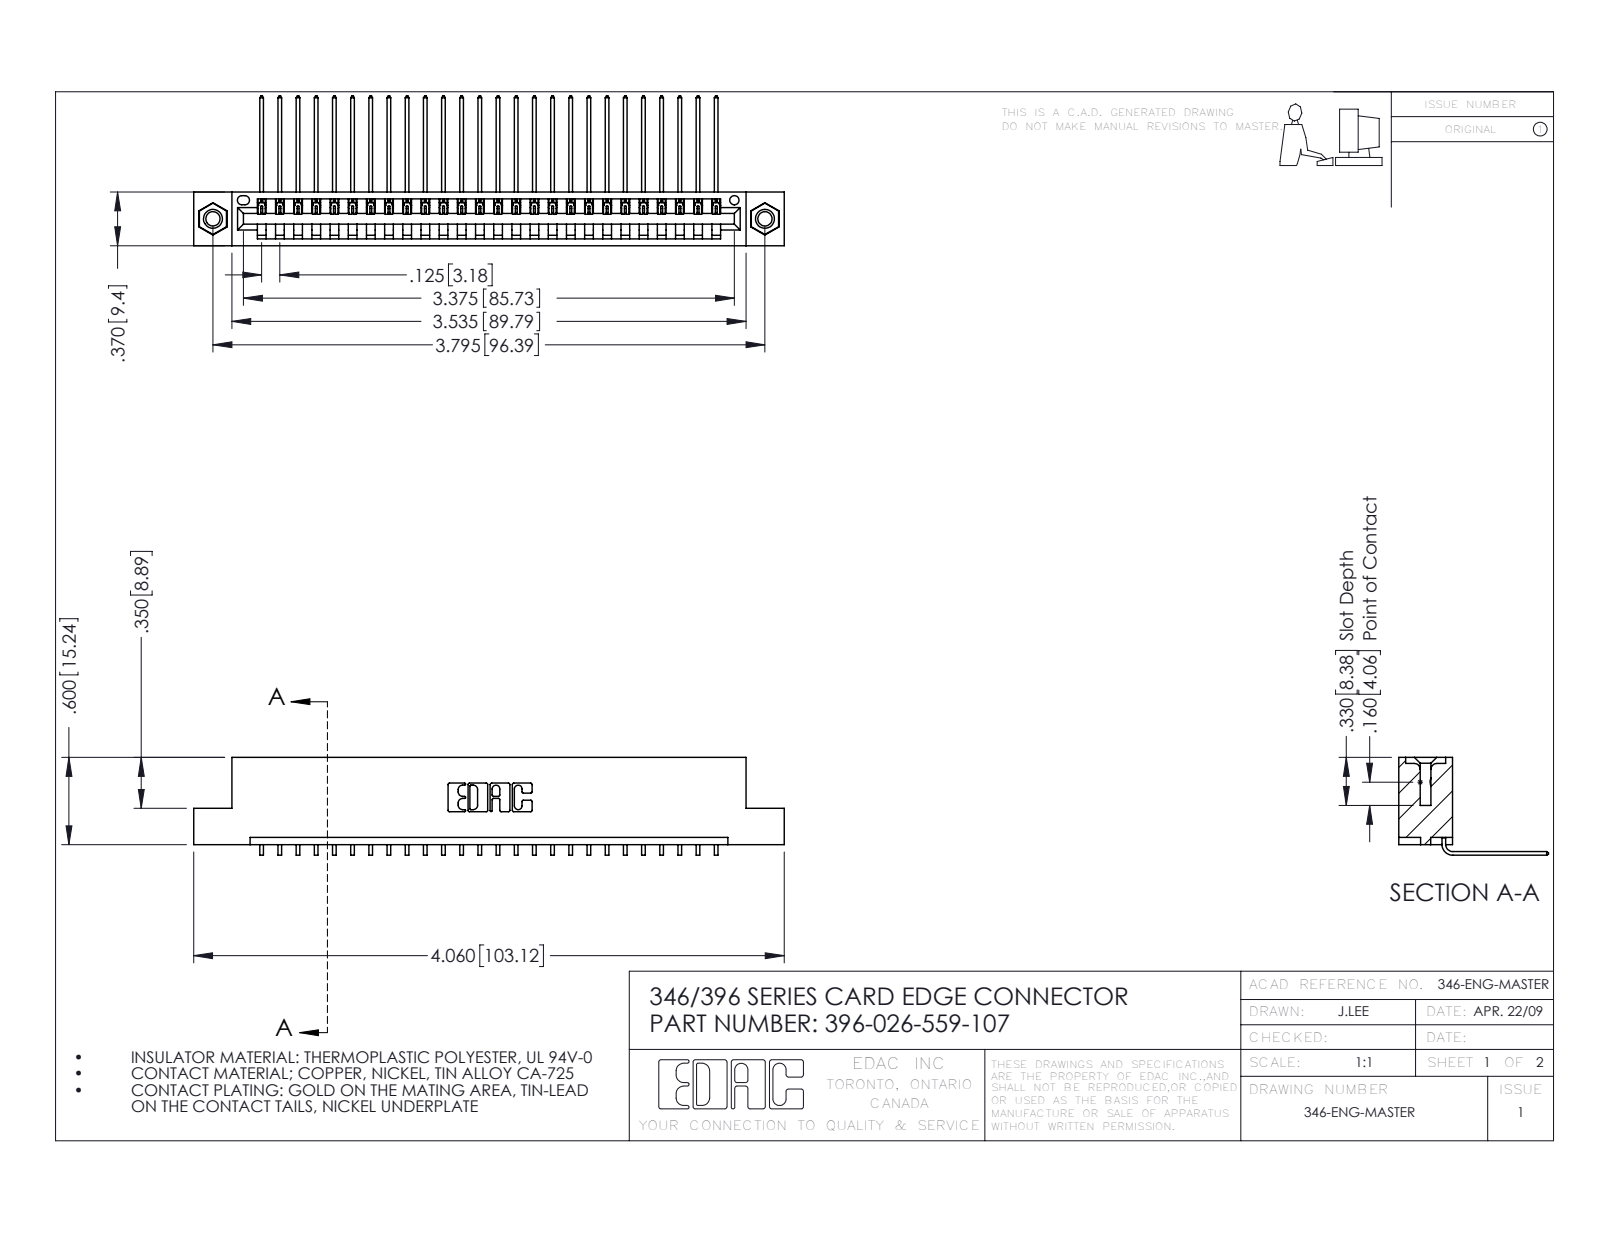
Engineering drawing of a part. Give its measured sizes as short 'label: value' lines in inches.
name: 345-292-001_558 559 Tail - 1; 346 Part_Flush Mounting Lugs - 0.156 Dia-TI; 396-026-559-107; 345-250-001_345-250-005-103
written by: SolidWorks 2016 (CONFIG_CONTROL_DESIGN)
unit: in
bodies: 29 solids, 1742 faces (1200 planar, 526 cylindrical, 16 other)
size: 4.06 × 1.03 × 0.673
volume: 0.6 in³; area: 19.64 in²
holes: 2× ⌀0.098, 2× ⌀0.125, 2× ⌀0.156, 1× ⌀0.064
bosses: 2× ⌀0.155
rounds: 52× R0.006, 22× R0.01, 6× R0.007, 6× R0.031, 3× R0.026, 2× R0.031, 2× R0.04, 1× R0.014
face distances: 0.048, 0.322, 0.37, 0.25, 0.072, 0.025, 0.298, 0.148, 0.222, 0.1
hole spacings: 0.246, 3.587, 3.795
